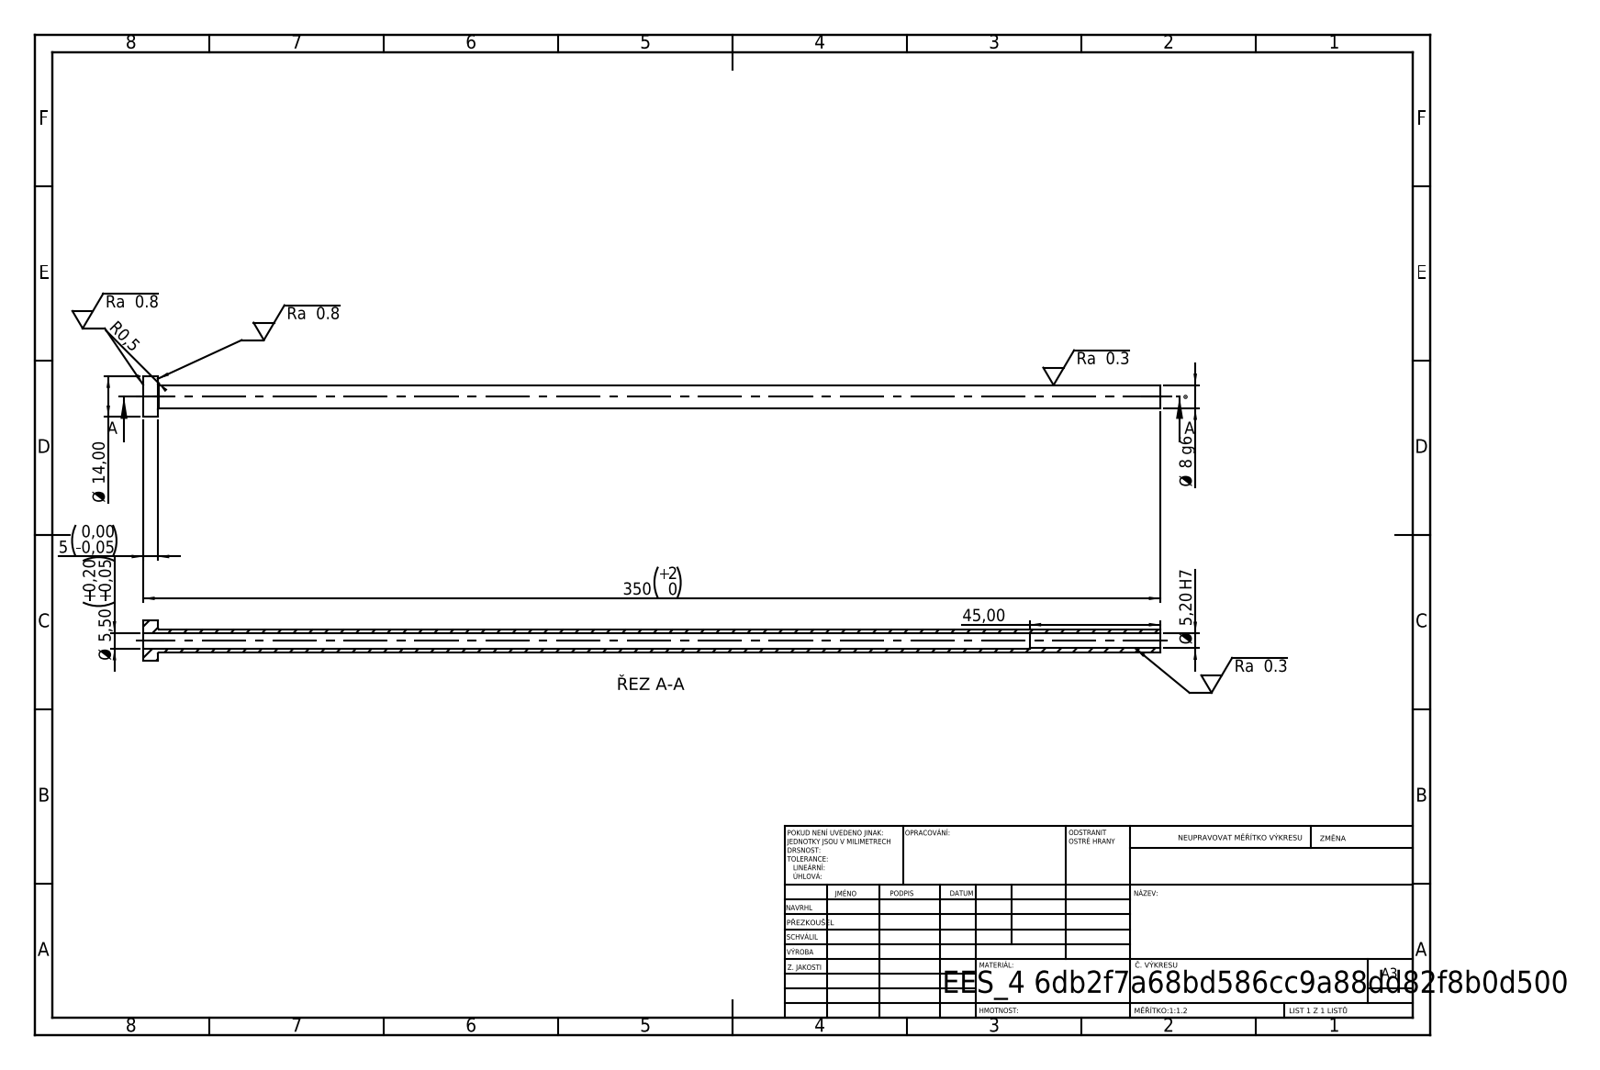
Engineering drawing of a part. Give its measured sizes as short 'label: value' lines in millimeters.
written by: SolidWorks 2019 (CONFIG_CONTROL_DESIGN)
unit: mm
bodies: 1 solid, 14 faces (4 planar, 8 cylindrical, 2 other)
size: 350 × 14 × 14
volume: 9 911 mm³; area: 15 156 mm²
holes: 1× ⌀5.2, 1× ⌀5.5
bosses: 1× ⌀14, 1× ⌀8
face distances: 5, 350, 345, 305, 300, 45
